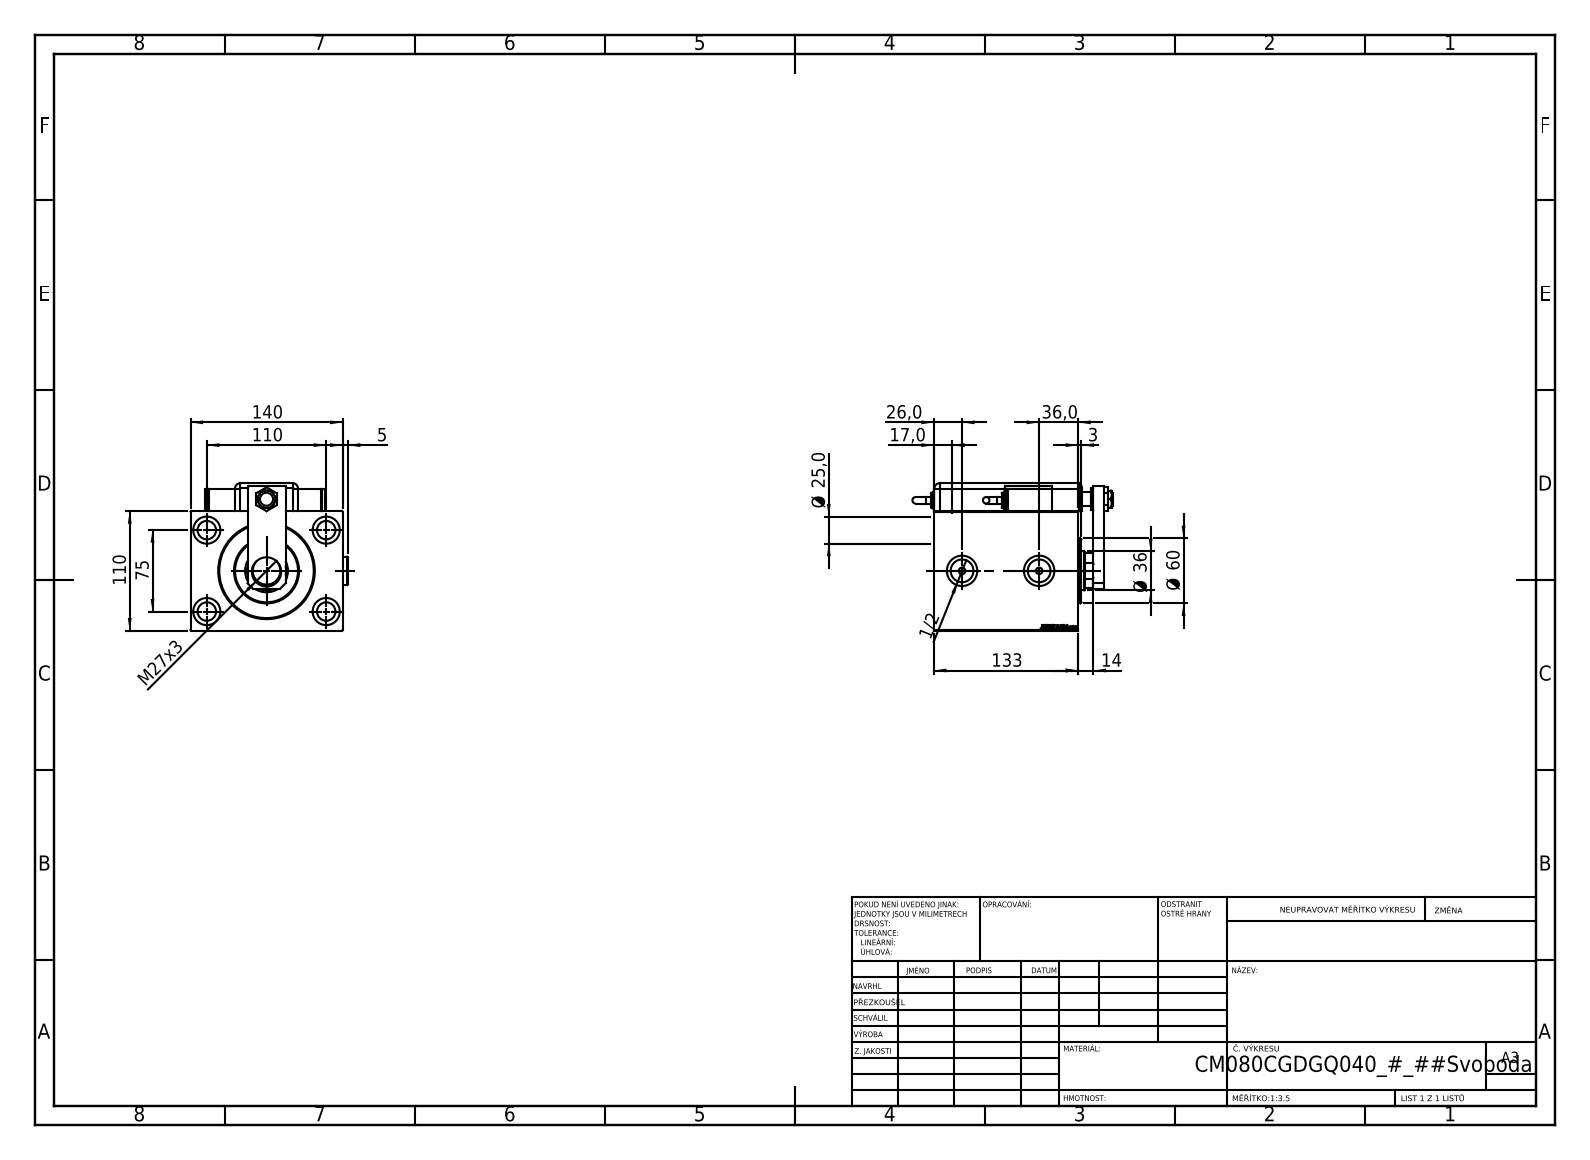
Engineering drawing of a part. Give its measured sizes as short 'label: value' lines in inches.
name: SWITCH_Q_FRONT_BACK; Zatka_OIL_PORT; SWITCH DIM A_G; ZARAZKA_Q (+7 more)
written by: SolidWorks 2019 (CONFIG_CONTROL_DESIGN)
unit: in
bodies: 15 solids, 1303 faces (649 planar, 133 cylindrical, 521 other)
size: 7.262 × 5.705 × 5.346
volume: 115 in³; area: 433.1 in²
holes: 4× ⌀0.669, 4× ⌀0.984, 2× ⌀0.157, 2× ⌀0.236, 2× ⌀0.315, 2× ⌀0.825, 2× ⌀1.102, 1× ⌀0.472, 1× ⌀0.512, 1× ⌀0.551, 1× ⌀1.004, 1× ⌀1.063
bosses: 3× ⌀0.787, 2× ⌀1.024, 2× ⌀0.63, 2× ⌀0.551, 2× ⌀0.236, 1× ⌀2.362
rounds: 9× R0.197, 1× R0.394, 1× R0.689
face distances: 4.331, 5.512, 0.118, 5.236, 0.827, 4.409, 0.551, 1.016, 5.346, 1.102
hole spacings: 2.621, 2.439, 2.599, 2.643, 2.953, 4.331, 4.615, 5.242
